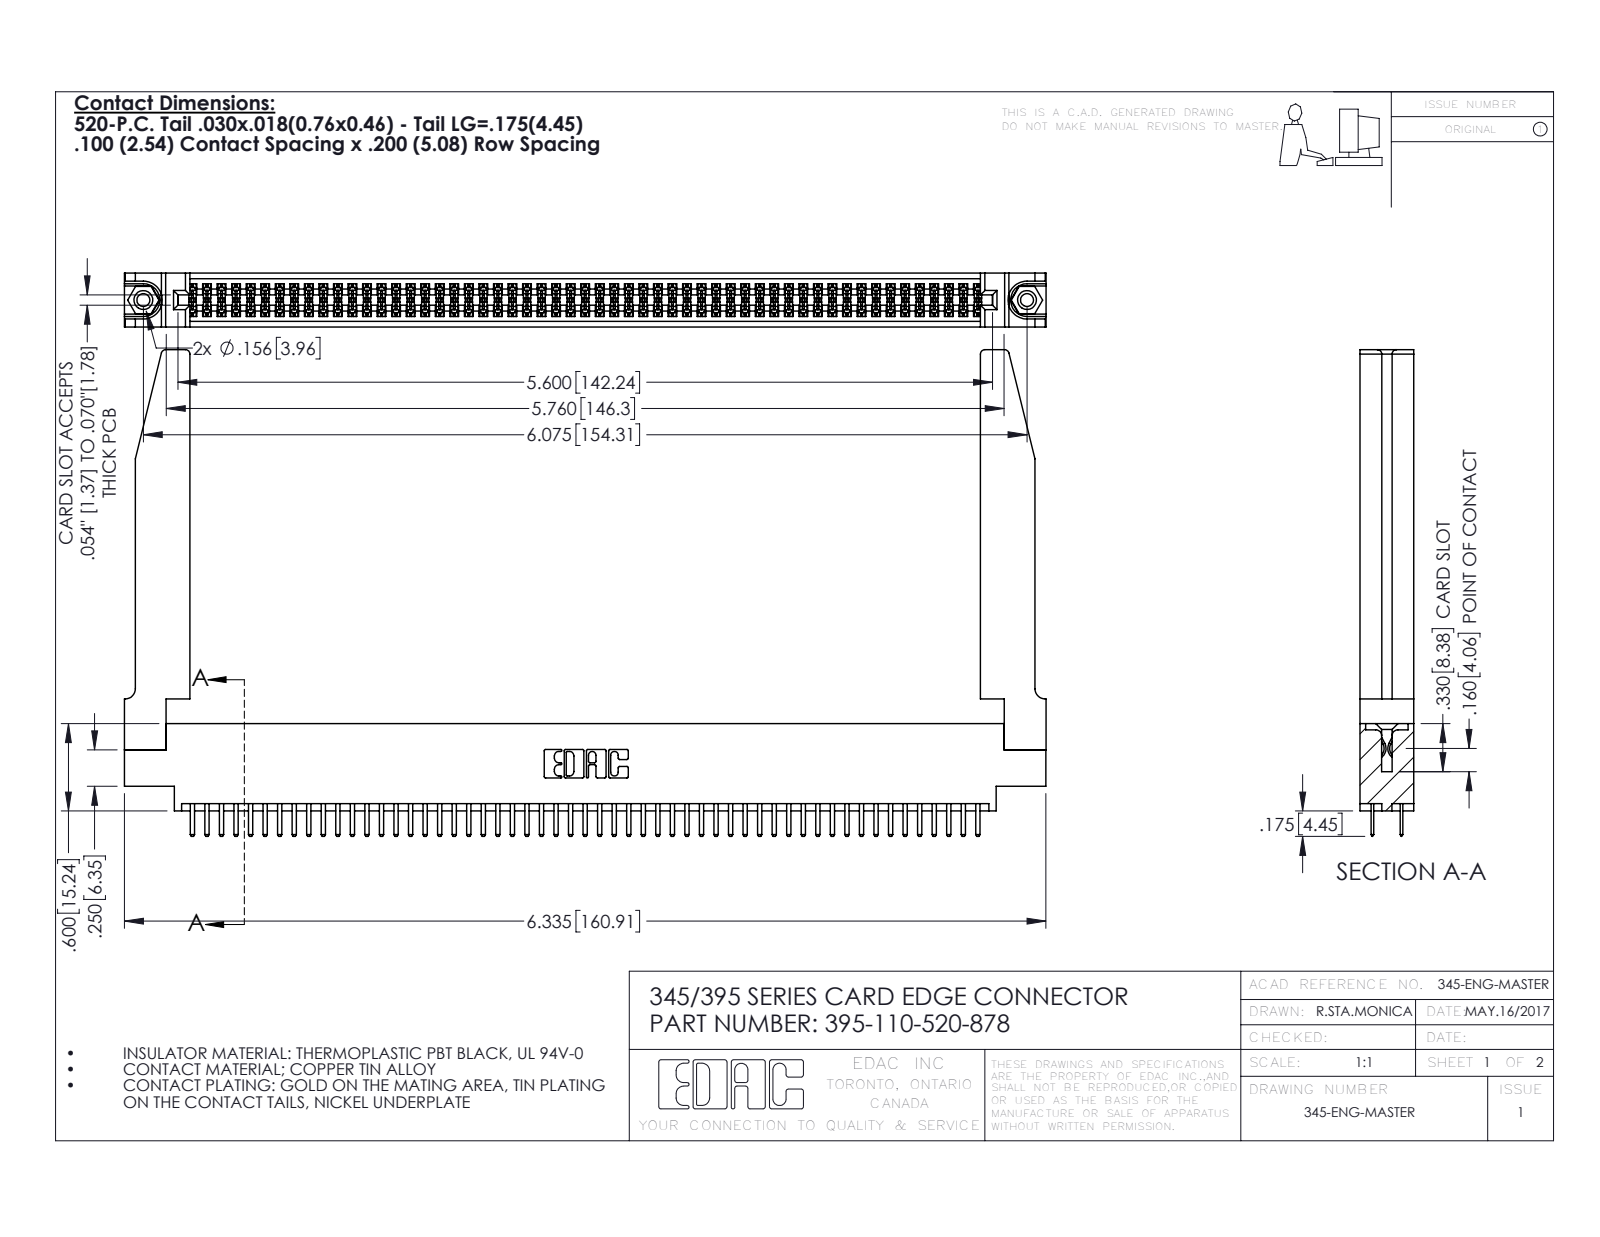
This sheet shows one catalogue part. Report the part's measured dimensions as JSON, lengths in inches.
{"part_name": "395-110-520-878; 345-292-001_345-293-120; 345 Part_0.170 Offset - 0.156 Dia-TH; 345-250-001_345-250-001-102 (+1 more)", "step_written_by": "SolidWorks 2016 (CONFIG_CONTROL_DESIGN)", "units": "inches", "bodies": {"solids": 115, "faces": 6304, "planar": 4076, "cylindrical": 2176, "other": 52}, "overall_size": [6.336, 3.345, 0.37], "volume_in3": 1.426, "surface_area_in2": 46.78, "round_holes": [[0.089, 2], [0.125, 2], [0.156, 2], [0.064, 1]], "round_bosses_or_shafts": [[0.155, 2]], "partial_cylinders_radius": [[0.006, 165], [0.01, 114], [0.01, 22], [0.03, 8], [0.007, 6], [0.031, 6], [0.026, 3], [0.014, 2]], "face_to_face_distances": [0.37, 0.072, 0.298, 0.2, 0.098, 0.272, 0.025, 0.225, 0.022, 0.072], "hole_center_spacings": [0.27, 5.839, 6.075]}
